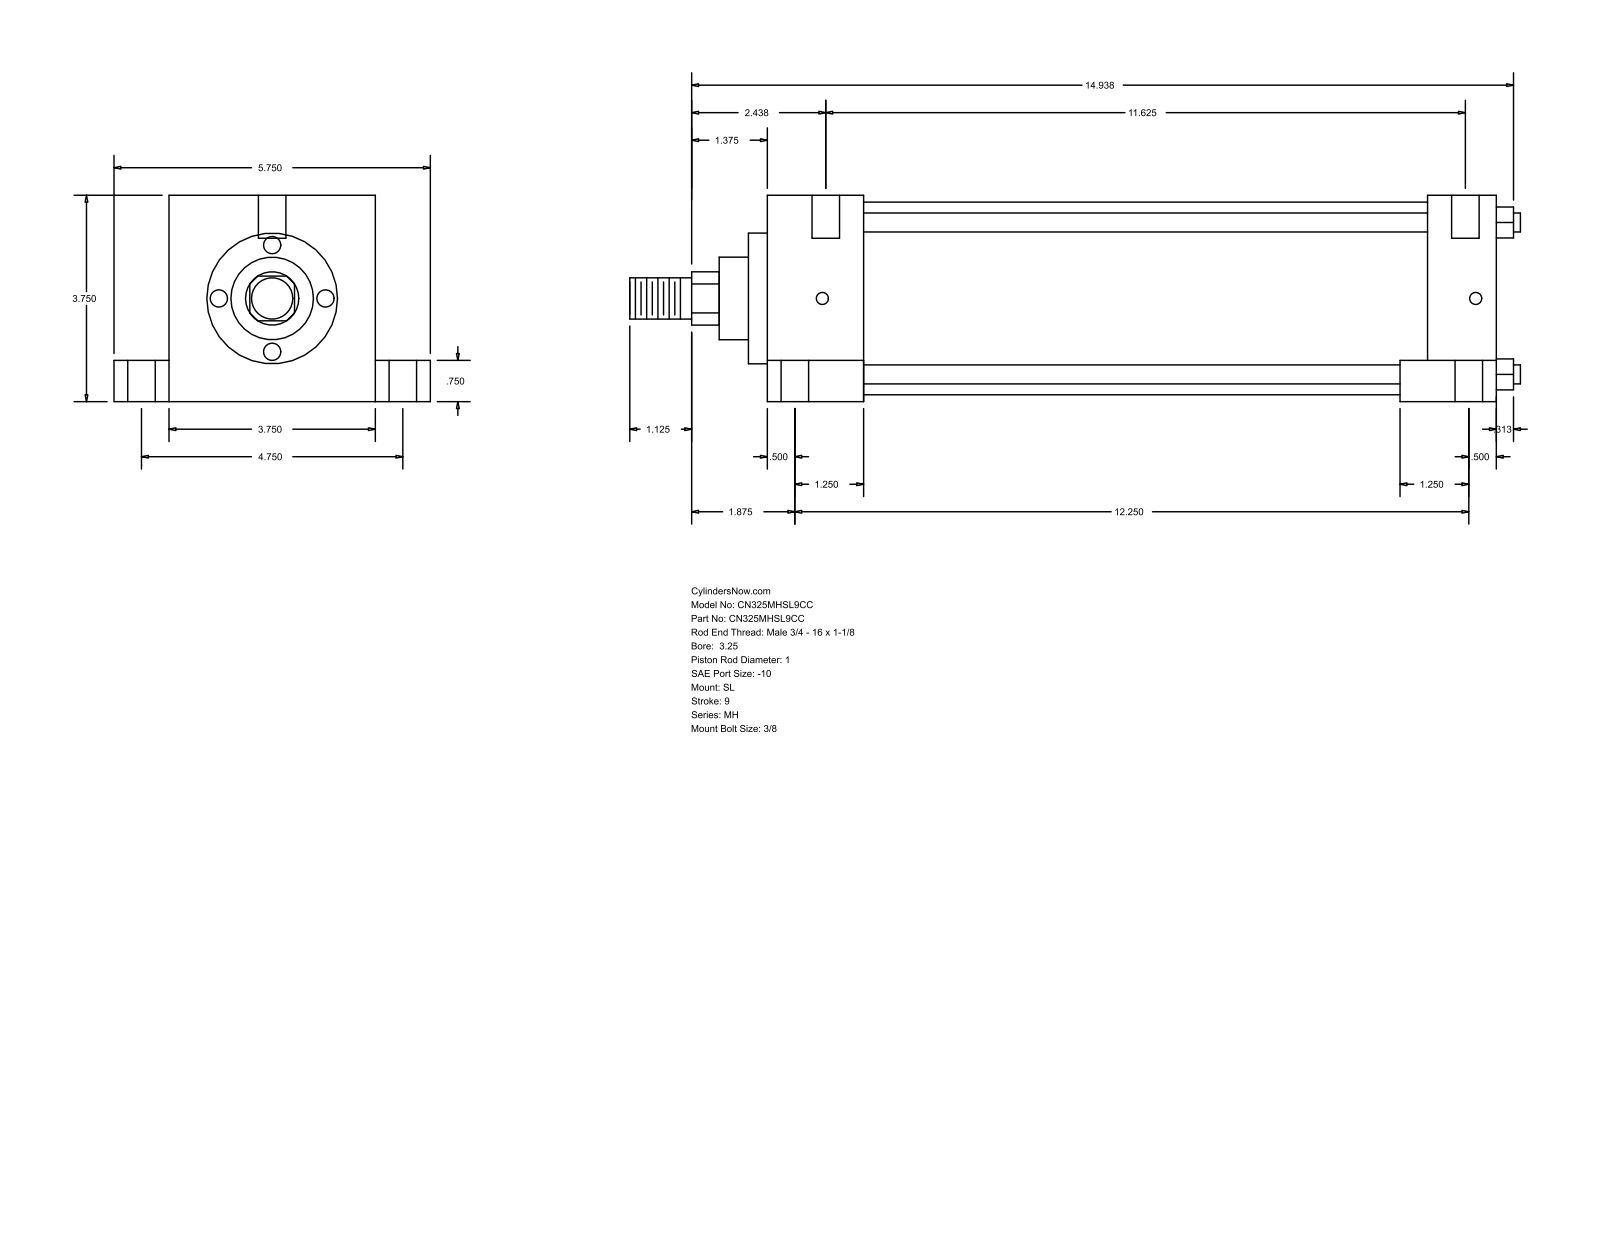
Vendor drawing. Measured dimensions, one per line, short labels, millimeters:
name: MH_SL__0325_1
written by: GSSL Pune (CONFIG_CONTROL_DESIGN)
unit: mm
bodies: 0 solids, 110 faces (77 planar, 33 cylindrical, 0 other)
size: 411.16 × 146.05 × 95.25
holes: 6× ⌀12.7, 4× ⌀5.56, 4× ⌀19.05
bosses: 4× ⌀8.76, 1× ⌀88.9, 1× ⌀60.33, 1× ⌀38.1, 1× ⌀25.4, 1× ⌀19.05
rounds: 1× R12.29
face distances: 95.24, 336.56, 44.46, 292.1, 25.41, 120.65, 19.05, 76.19, 304.81, 260.35
hole spacings: 60.35, 60.41, 61.65, 62, 120.66, 301.62, 302.93, 304.48
